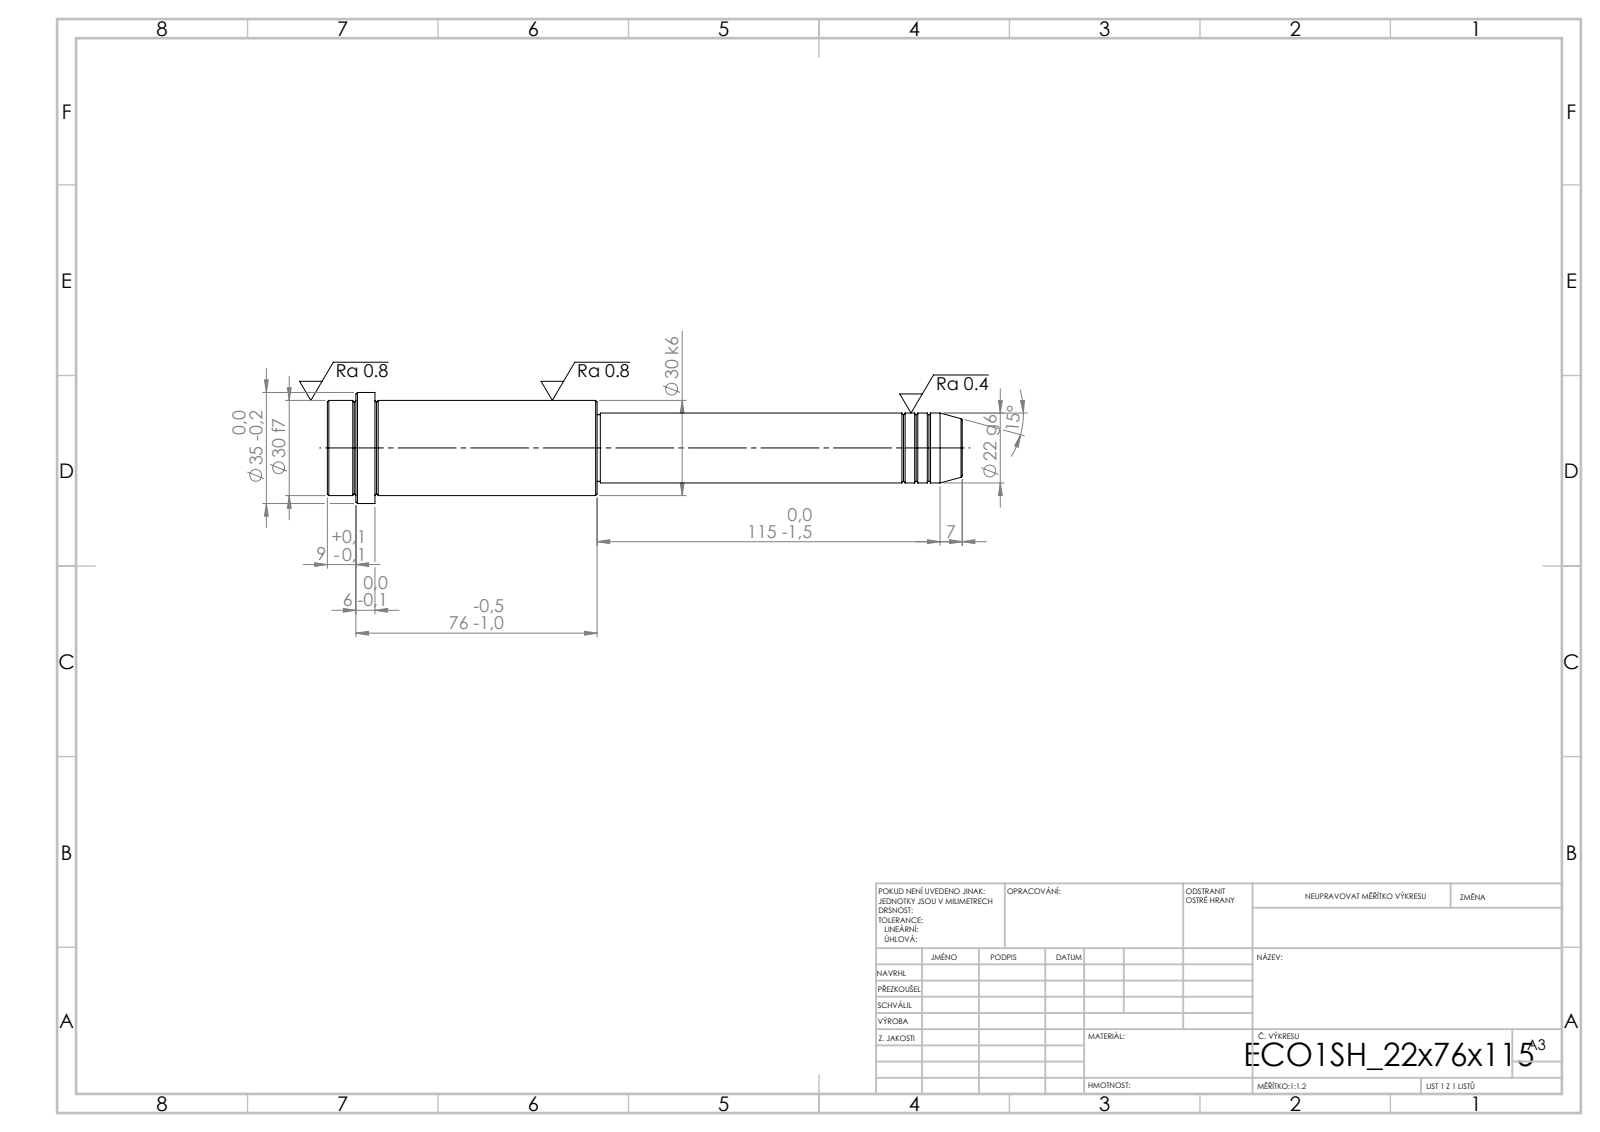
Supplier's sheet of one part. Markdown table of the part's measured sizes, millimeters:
| quantity | value |
| --- | --- |
| STEP written by | SolidWorks 2019 (CONFIG_CONTROL_DESIGN) |
| units | millimeters |
| bodies | 1 solid, 52 faces (6 planar, 16 cylindrical, 30 other) |
| overall size | 200 × 35 × 35 |
| volume | 104 677 mm³ |
| surface area | 18 013 mm² |
| round bosses / shafts (diameter × count) | 35 × 1, 30 × 1, 22 × 1, 21 × 1 |
| main face-to-face distances | 85, 70, 15, 115, 185, 200, 191, 76, 6, 9 |
